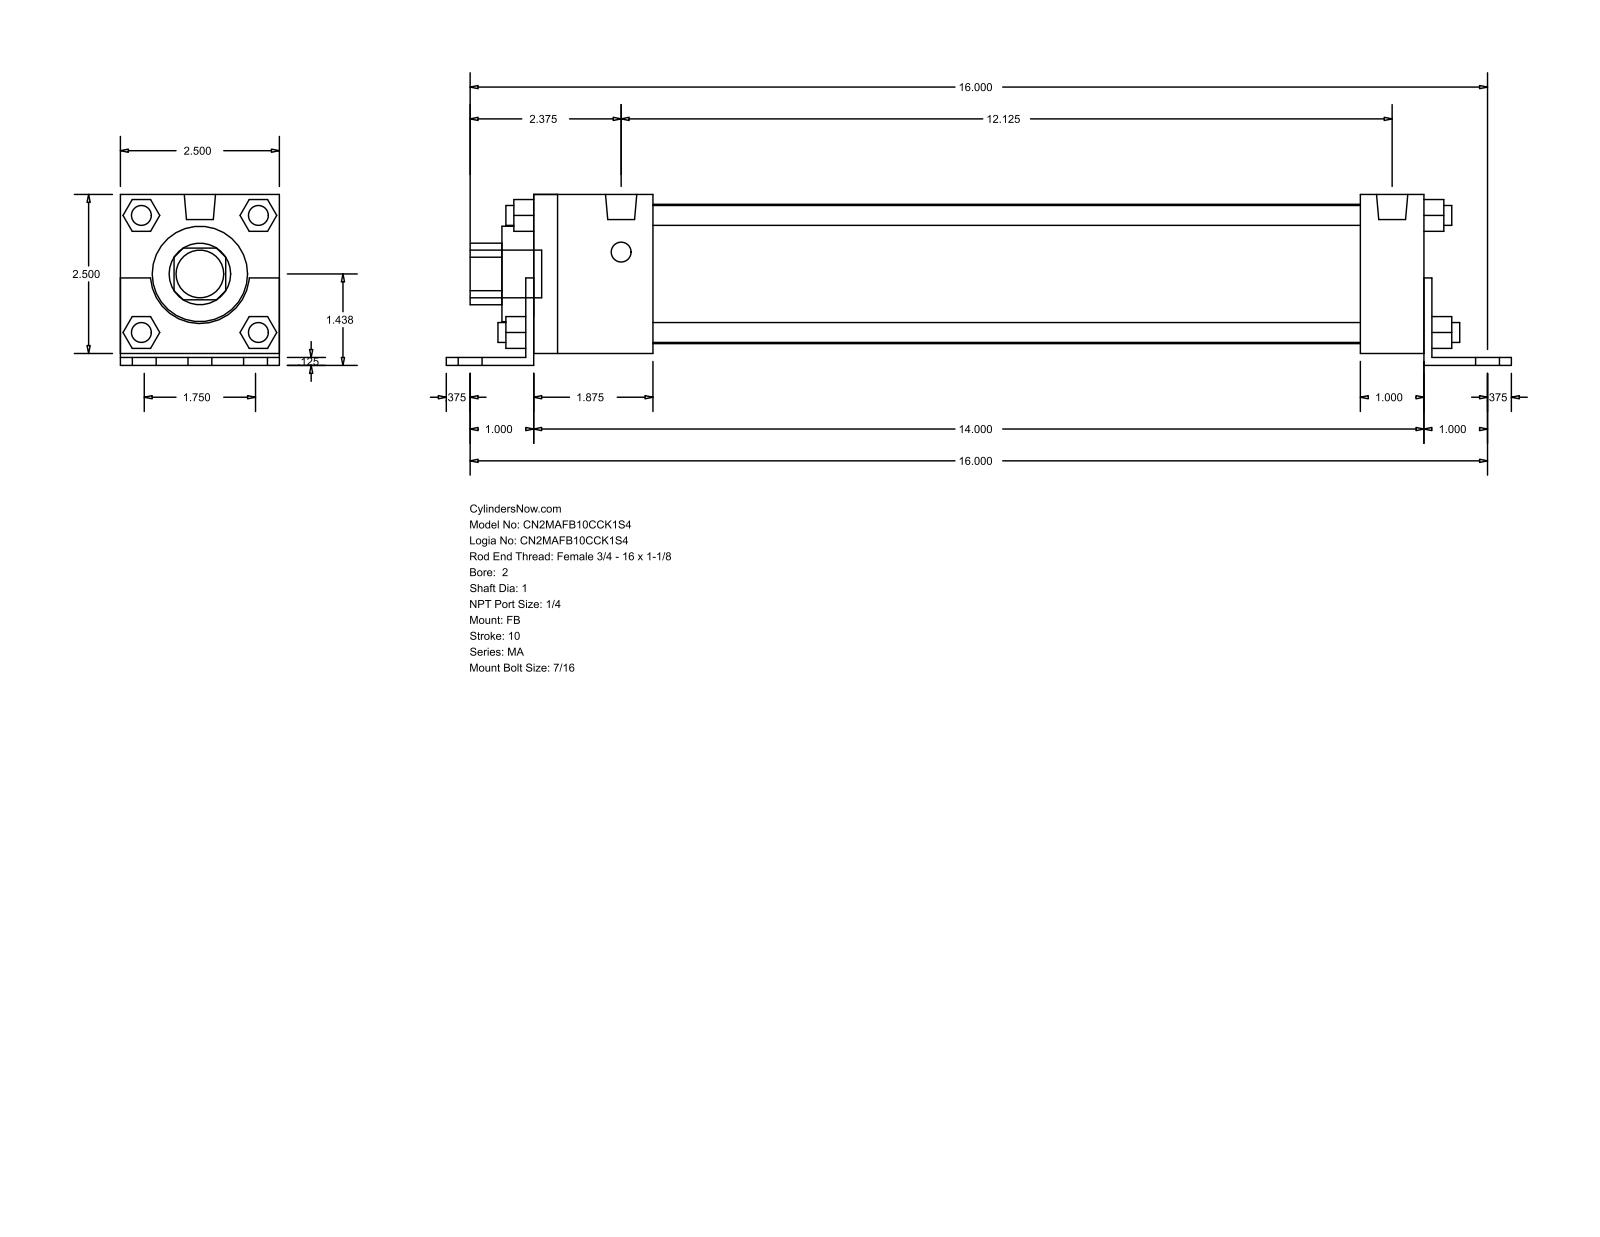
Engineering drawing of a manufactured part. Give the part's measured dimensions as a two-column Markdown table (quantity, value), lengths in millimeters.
| quantity | value |
| --- | --- |
| part name | MA_FB__0200_1 |
| STEP written by | GSSL Pune (CONFIG_CONTROL_DESIGN) |
| units | millimeters |
| bodies | 0 solids, 140 faces (105 planar, 35 cylindrical, 0 other) |
| overall size | 425.45 × 68.26 × 63.5 |
| round holes (diameter × count) | 25.4 × 1, 38.1 × 1, 55.63 × 1 |
| round bosses / shafts (diameter × count) | 7.94 × 8, 11.11 × 6, 12.49 × 2, 19.05 × 1 |
| partial cylindrical surfaces (radius × count) | 12.29 × 1, 19.81 × 1 |
| main face-to-face distances | 63.5, 3.17, 4.76, 68.26, 1.59, 65.09, 12.7, 3.18, 355.6, 358.78 |
